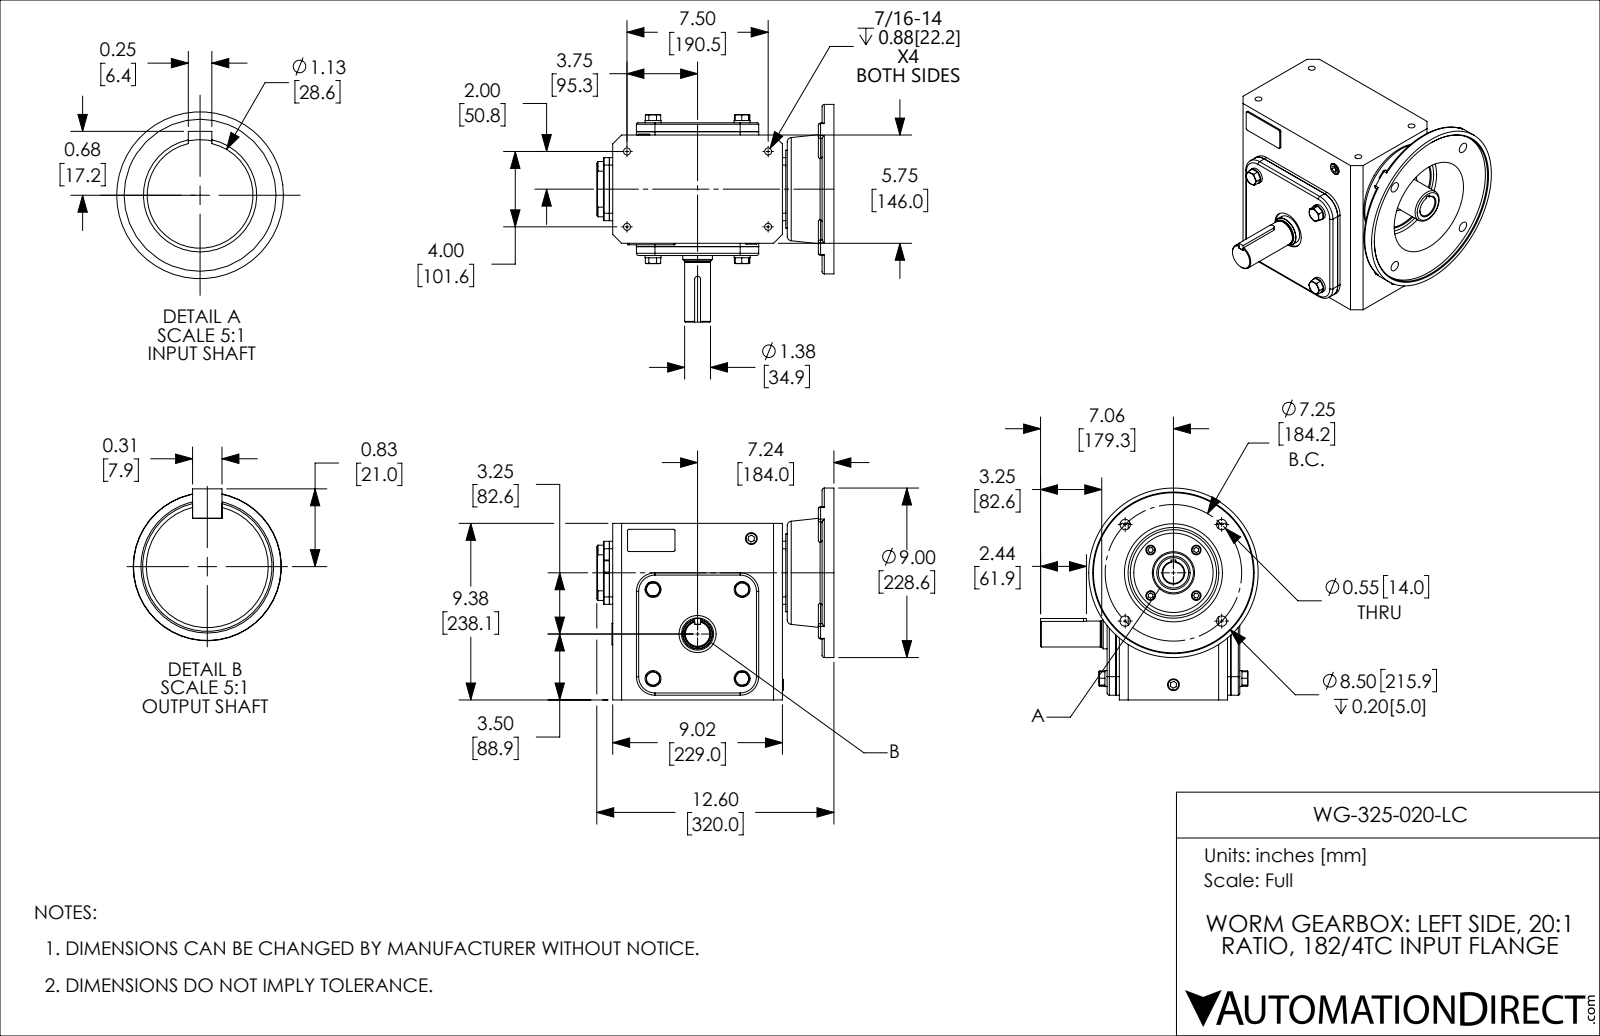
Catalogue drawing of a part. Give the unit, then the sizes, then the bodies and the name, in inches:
Units: inches
Overall size (bounding box): 12.598 × 11.559 × 11.25
Round holes (diameter × count): ⌀0.354 ×4, ⌀0.368 ×4, ⌀0.551 ×4, ⌀0.628 ×3, ⌀0.591 ×1, ⌀0.978 ×1, ⌀1.125 ×1, ⌀1.181 ×1, ⌀1.969 ×1, ⌀2.244 ×1, ⌀2.441 ×1, ⌀2.756 ×1
Round bosses / shafts (diameter × count): ⌀0.846 ×4, ⌀0.512 ×4, ⌀9 ×1, ⌀4.134 ×1, ⌀2.835 ×1, ⌀1.772 ×1, ⌀1.575 ×1, ⌀1.375 ×1
Partial cylindrical surfaces — rounded edges, fillets, slot ends (radius × count): R0.118 ×14, R0.079 ×11, R0.394 ×4, R0.906 ×4, R0.984 ×4, R0.02 ×2, R0.039 ×2, R0.156 ×1
Main face-to-face distances: 0.079, 0.177, 6.496, 0.394, 6.969, 0.472, 6.575, 6.398, 0.571, 0.65
Hole centre spacings: 4.009, 1.713, 1.913, 2.422, 3.625, 5.127, 5.338, 2.372
Volume: 529.7 in³ · Surface area: 1 026 in²
Bodies: 40 solids, 653 faces (336 planar, 195 cylindrical, 122 other)
Part name (STEP PRODUCT): WG-325-020-LC
STEP written by: SolidWorks 2017 (AUTOMOTIVE_DESIGN)
